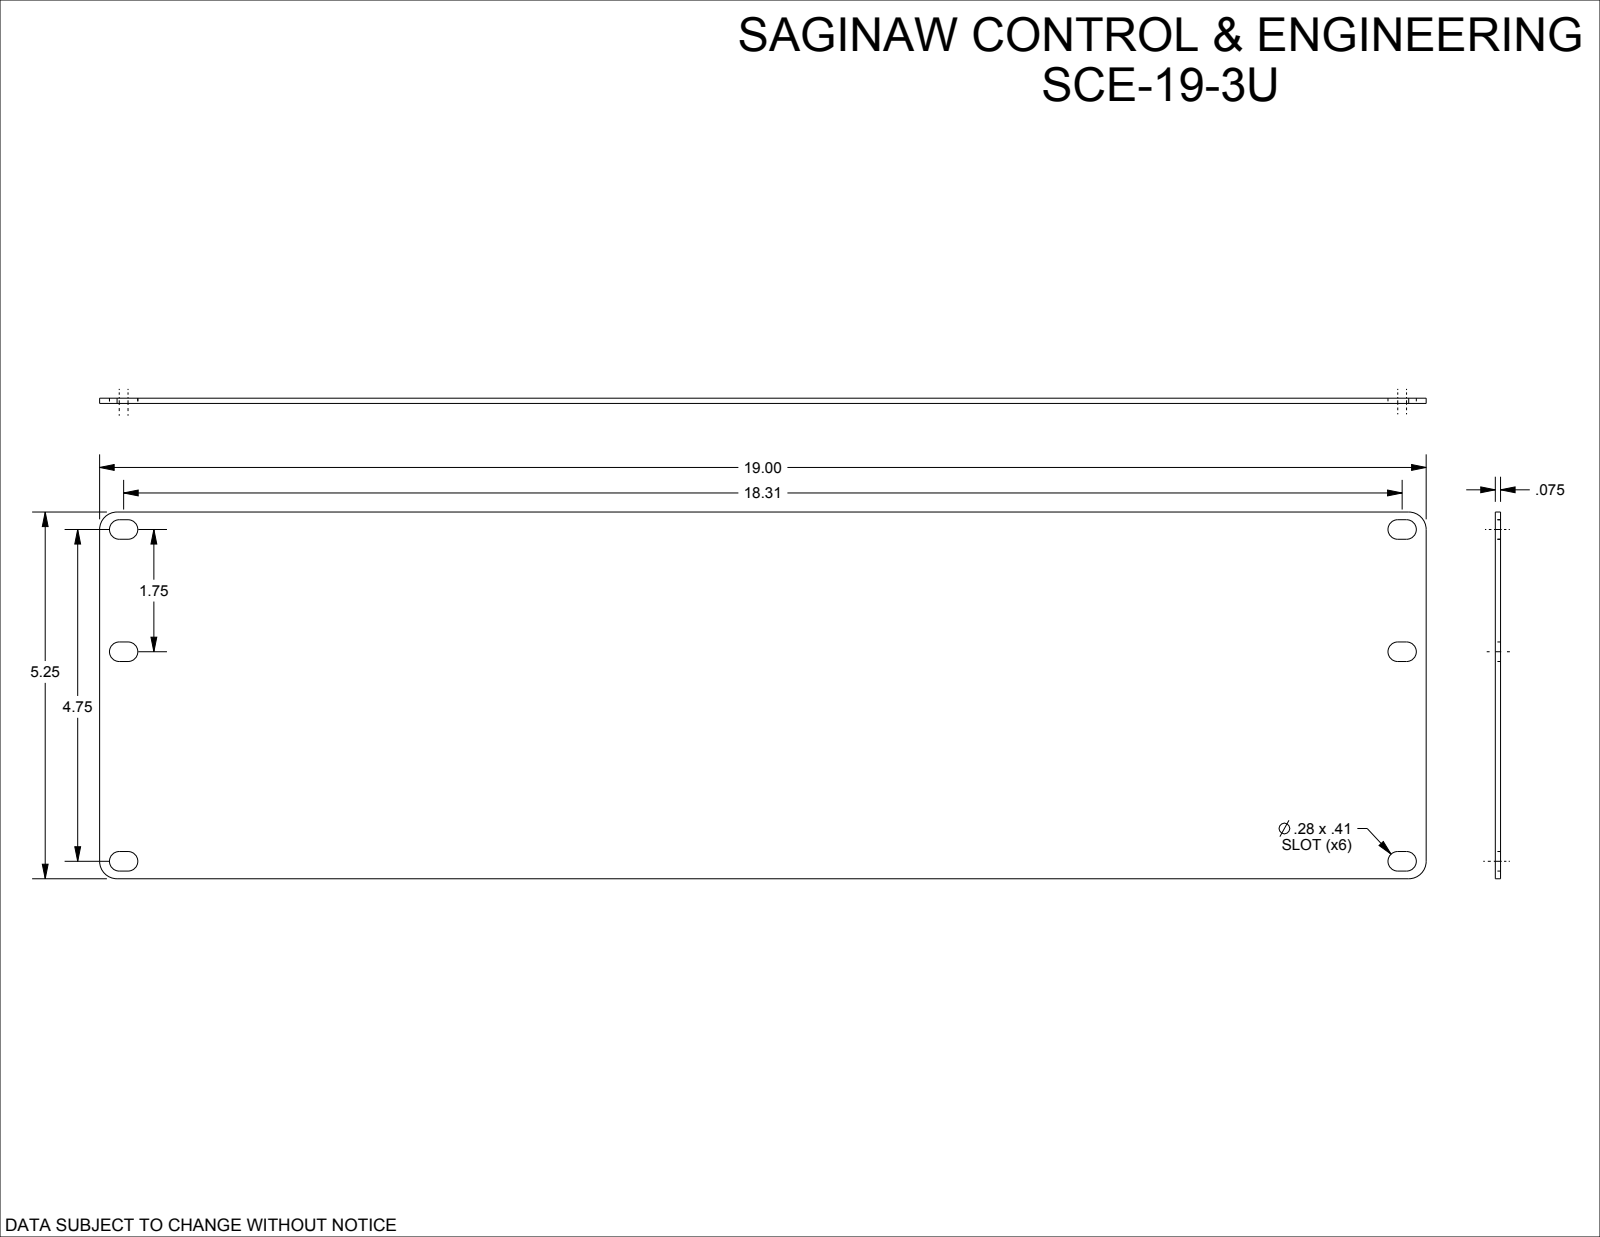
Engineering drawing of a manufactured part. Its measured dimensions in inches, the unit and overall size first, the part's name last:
Units: inches
Overall size (bounding box): 19 × 5.25 × 0.075
Partial cylindrical surfaces — rounded edges, fillets, slot ends (radius × count): R0.14 ×10, R0.25 ×4, R0.14 ×2
Main face-to-face distances: 0.075, 5.25, 19, 0.28, 0.11, 0.39, 4.86, 5.14, 3, 4.75
Volume: 7.434 in³ · Surface area: 202.3 in²
Bodies: 1 solid, 34 faces (18 planar, 16 cylindrical, 0 other)
Part name (STEP PRODUCT): SCE-19-3U
STEP written by: SolidWorks 2019 (CONFIG_CONTROL_DESIGN)
